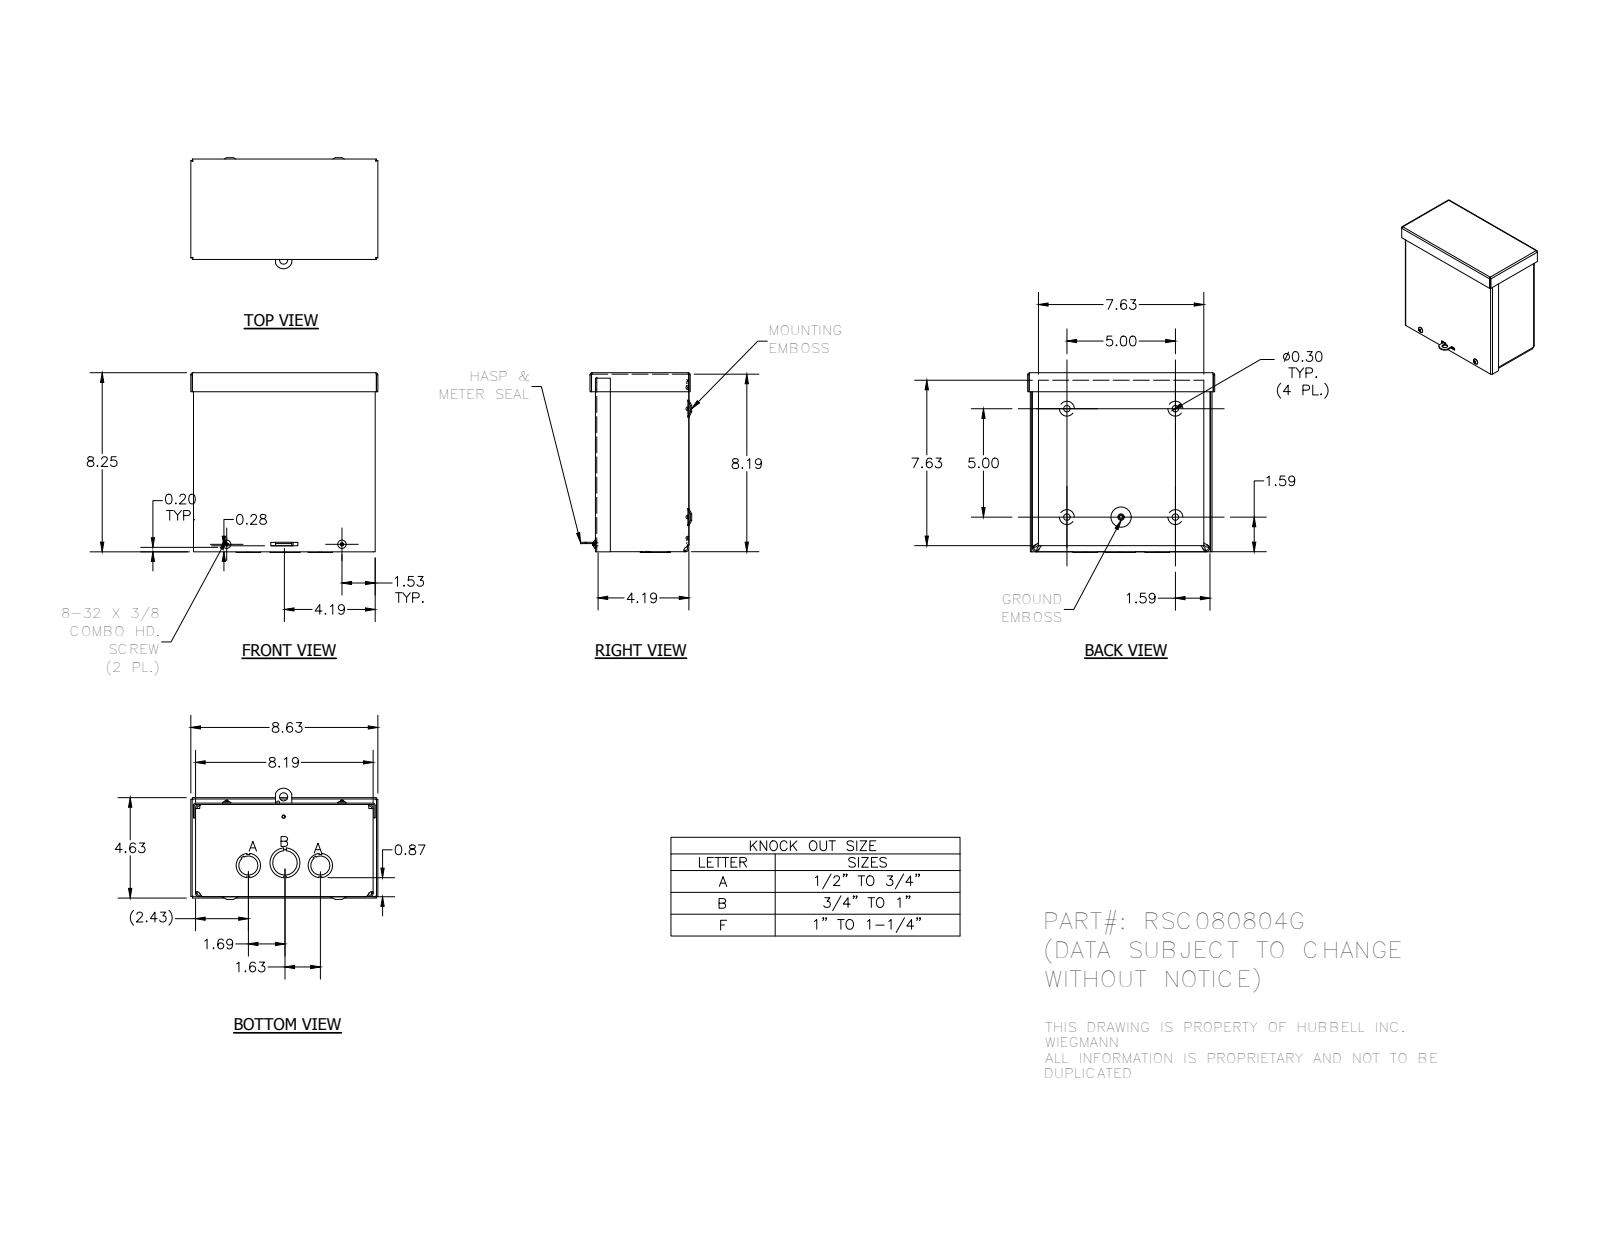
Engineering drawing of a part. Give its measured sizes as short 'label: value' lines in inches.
name: RSC080804G_WRAP; RSC0808G_LID; RSC0804G_CAP; 3183 (+4 more)
written by: Autodesk Inventor 2014 (AUTOMOTIVE_DESIGN)
unit: in
bodies: 7 solids, 503 faces (238 planar, 121 cylindrical, 144 other)
size: 8.625 × 8.28 × 5.125
volume: 23.23 in³; area: 762.8 in²
holes: 4× ⌀0.3, 4× ⌀0.313, 3× ⌀1.125, 2× ⌀0.125, 2× ⌀0.148, 2× ⌀0.875, 1× ⌀0.156, 1× ⌀0.165, 1× ⌀0.375, 1× ⌀1.375
bosses: 2× ⌀0.384, 2× ⌀0.164, 1× ⌀0.228
rounds: 10× R0.01, 8× R0.031, 8× R0.093, 8× R0.125, 8× R0.187, 4× R0.021, 4× R0.031, 4× R0.055
face distances: 0.062, 8.126, 0.062, 4.249, 4.187, 8.188, 0.063, 0.124, 4.312, 4.25
hole spacings: 5, 1.072, 1.261, 2.5, 5.313, 5.59, 6.063, 6.253
